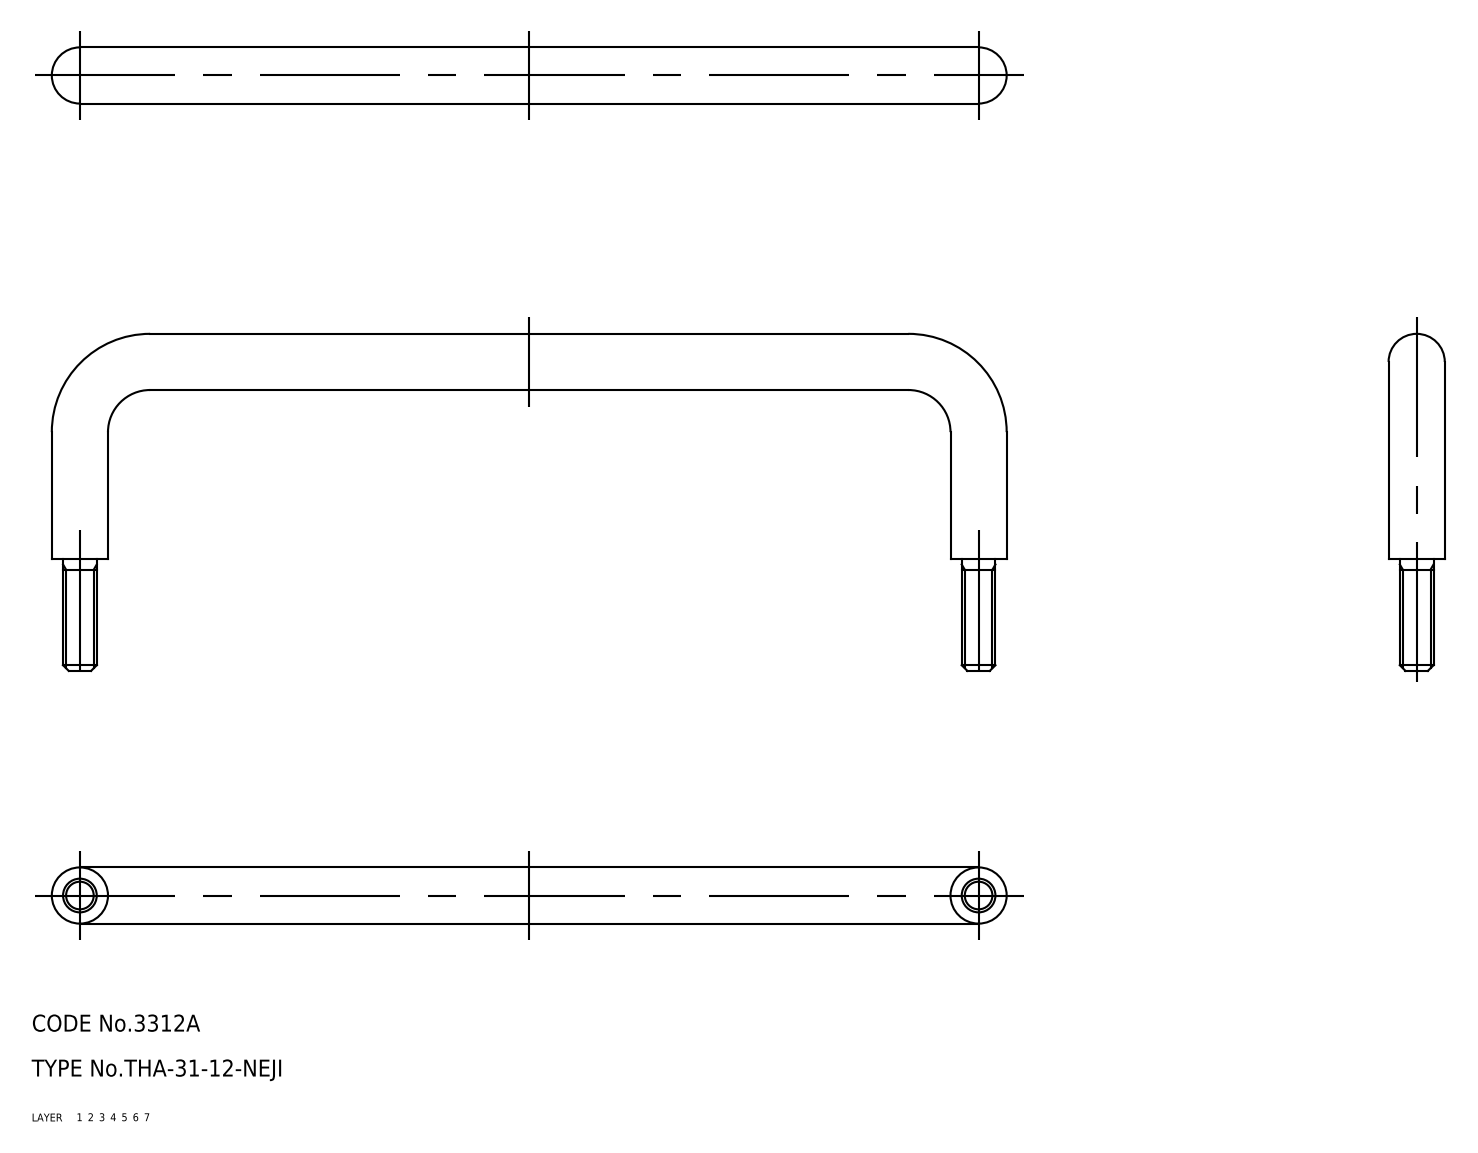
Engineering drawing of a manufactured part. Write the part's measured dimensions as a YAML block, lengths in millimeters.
part_name: "pull"
step_written_by: "CADfix (AUTOMOTIVE_DESIGN)"
units: millimeters
bodies: {solids: 1, faces: 22, planar: 0, cylindrical: 0, other: 22}
overall_size: [170, 60, 10]
volume: 18315
surface_area: 7779
